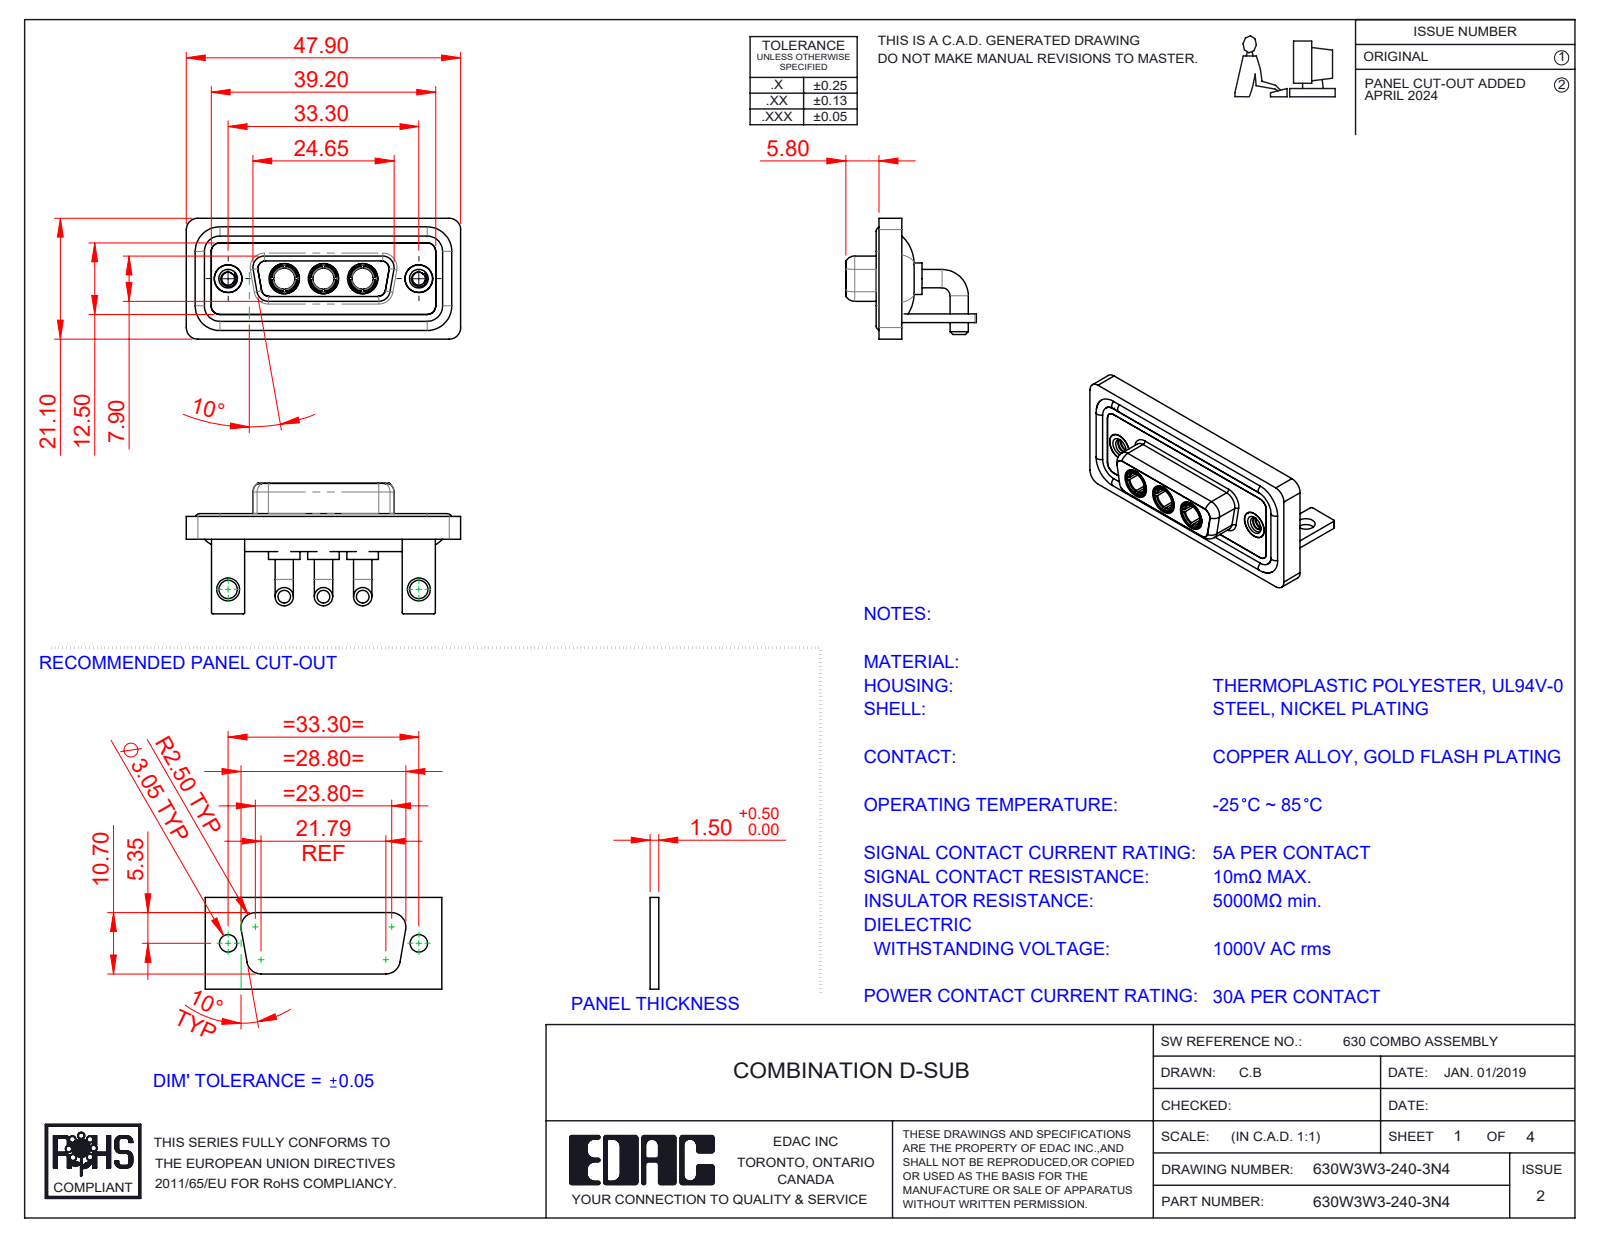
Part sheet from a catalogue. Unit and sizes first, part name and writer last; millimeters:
Units: millimetres
Overall size (bounding box): 47.9 × 22.8 × 21.1
Round holes (diameter × count): ⌀4.85 ×5, ⌀3.7 ×3, ⌀5.3 ×3, ⌀2.26 ×2, ⌀3.2 ×2, ⌀4 ×2, ⌀4.05 ×2, ⌀5 ×2
Round bosses / shafts (diameter × count): ⌀3.2 ×6, ⌀1.6 ×4, ⌀5.5 ×3, ⌀5.2 ×3, ⌀4.96 ×3, ⌀4.75 ×3, ⌀3.75 ×3, ⌀4.95 ×2
Partial cylindrical surfaces — rounded edges, fillets, slot ends (radius × count): R2 ×21, R1.5 ×18, R0.25 ×16, R1.35 ×12, R1.6 ×8, R0.5 ×5, R0.6 ×4, R0.65 ×4
Main face-to-face distances: 0.4, 2.9, 1.5, 1.8, 3.7, 1.1, 4.1, 1.6, 2.5, 1.4
Hole centre spacings: 6.85, 9.8, 16.65, 23.5, 33.3, 13.7
Volume: 6 630 mm³ · Surface area: 10 762 mm²
Bodies: 15 solids, 668 faces (212 planar, 287 cylindrical, 169 other)
Part name (STEP PRODUCT): 630Combo Waterproof Housing_15 Contacts; 630W3W3-140-3N4; 630Combo Stabilizer Bracket_50 Contacts; 630Combo Shell Rear_15 Contacts (+4 more)
STEP written by: SolidWorks 2023 (CONFIG_CONTROL_DESIGN)
